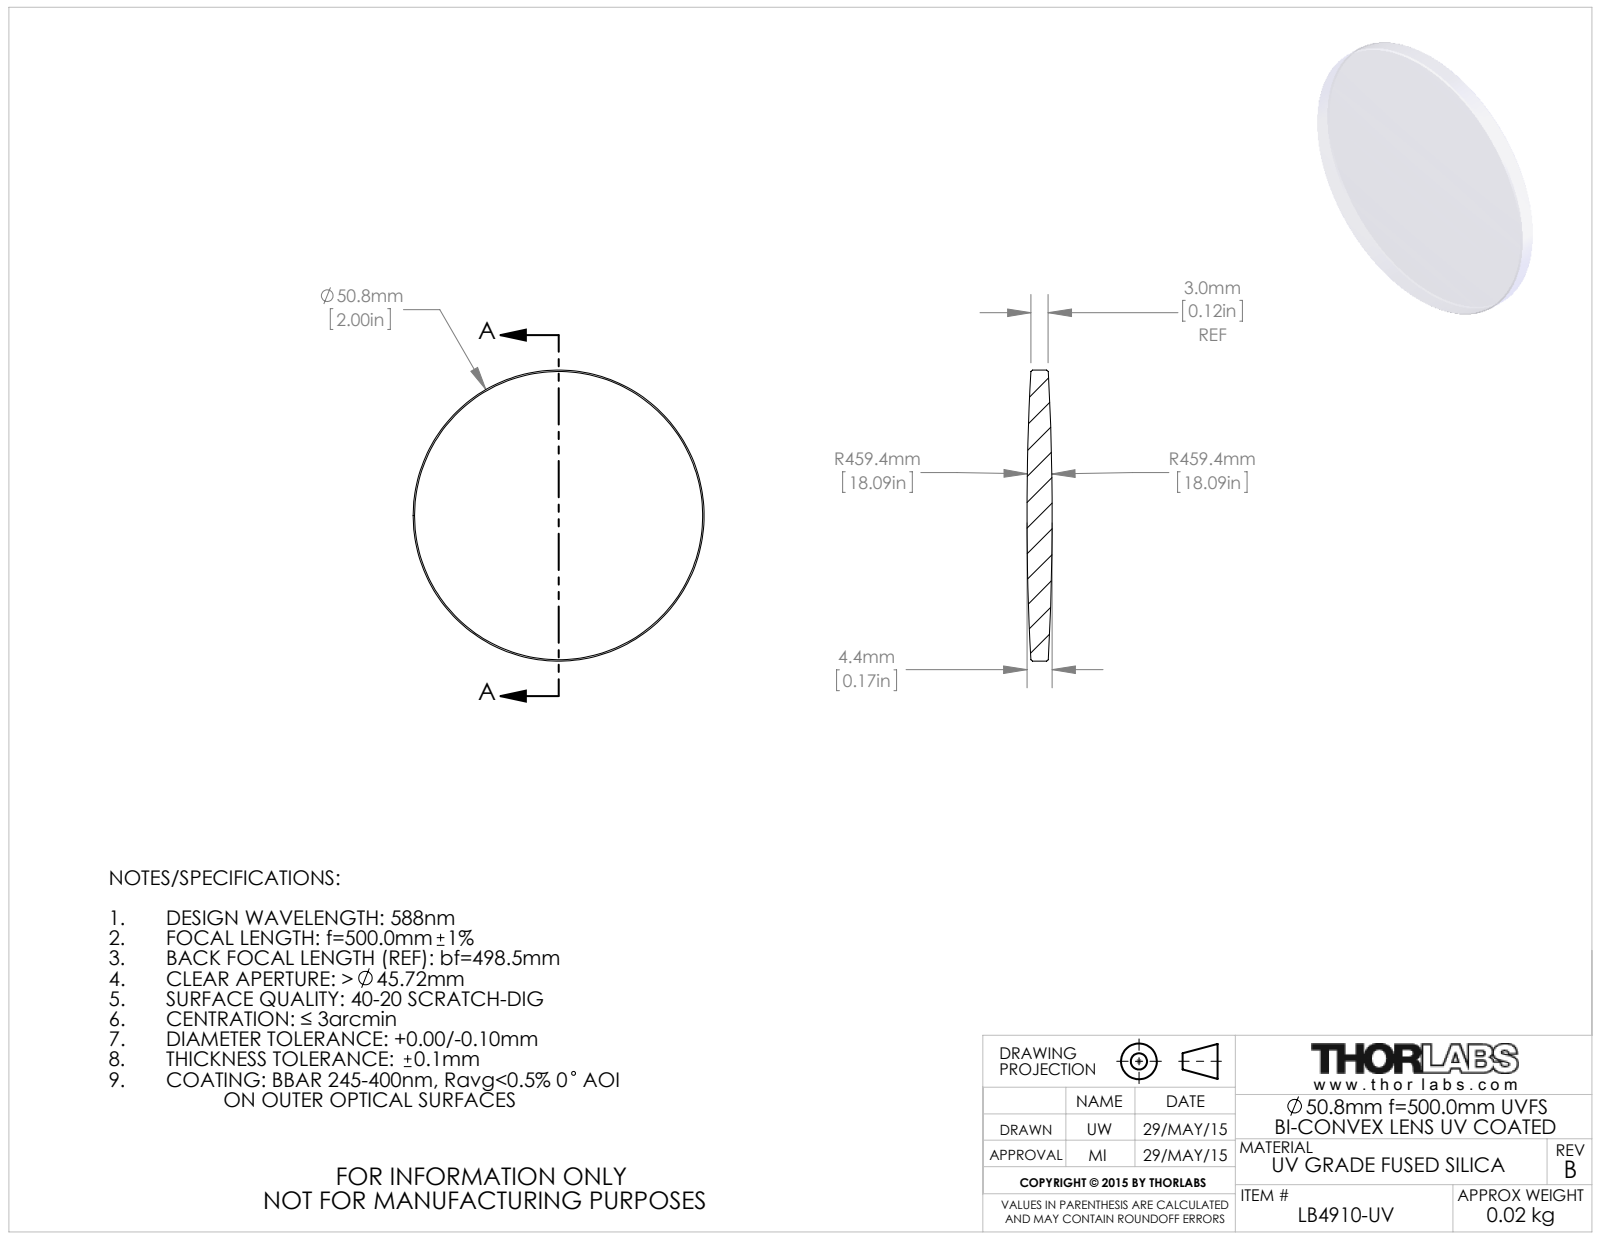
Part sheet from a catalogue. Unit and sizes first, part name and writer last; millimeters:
Units: millimetres
Overall size (bounding box): 50.8 × 50.8 × 4.4
Round bosses / shafts (diameter × count): ⌀50.8 ×1
Volume: 7 484 mm³ · Surface area: 4 491 mm²
Bodies: 1 solid, 10 faces (0 planar, 2 cylindrical, 8 other)
Part name (STEP PRODUCT): 4338-E0W
STEP written by: SolidWorks 2014 (CONFIG_CONTROL_DESIGN)
